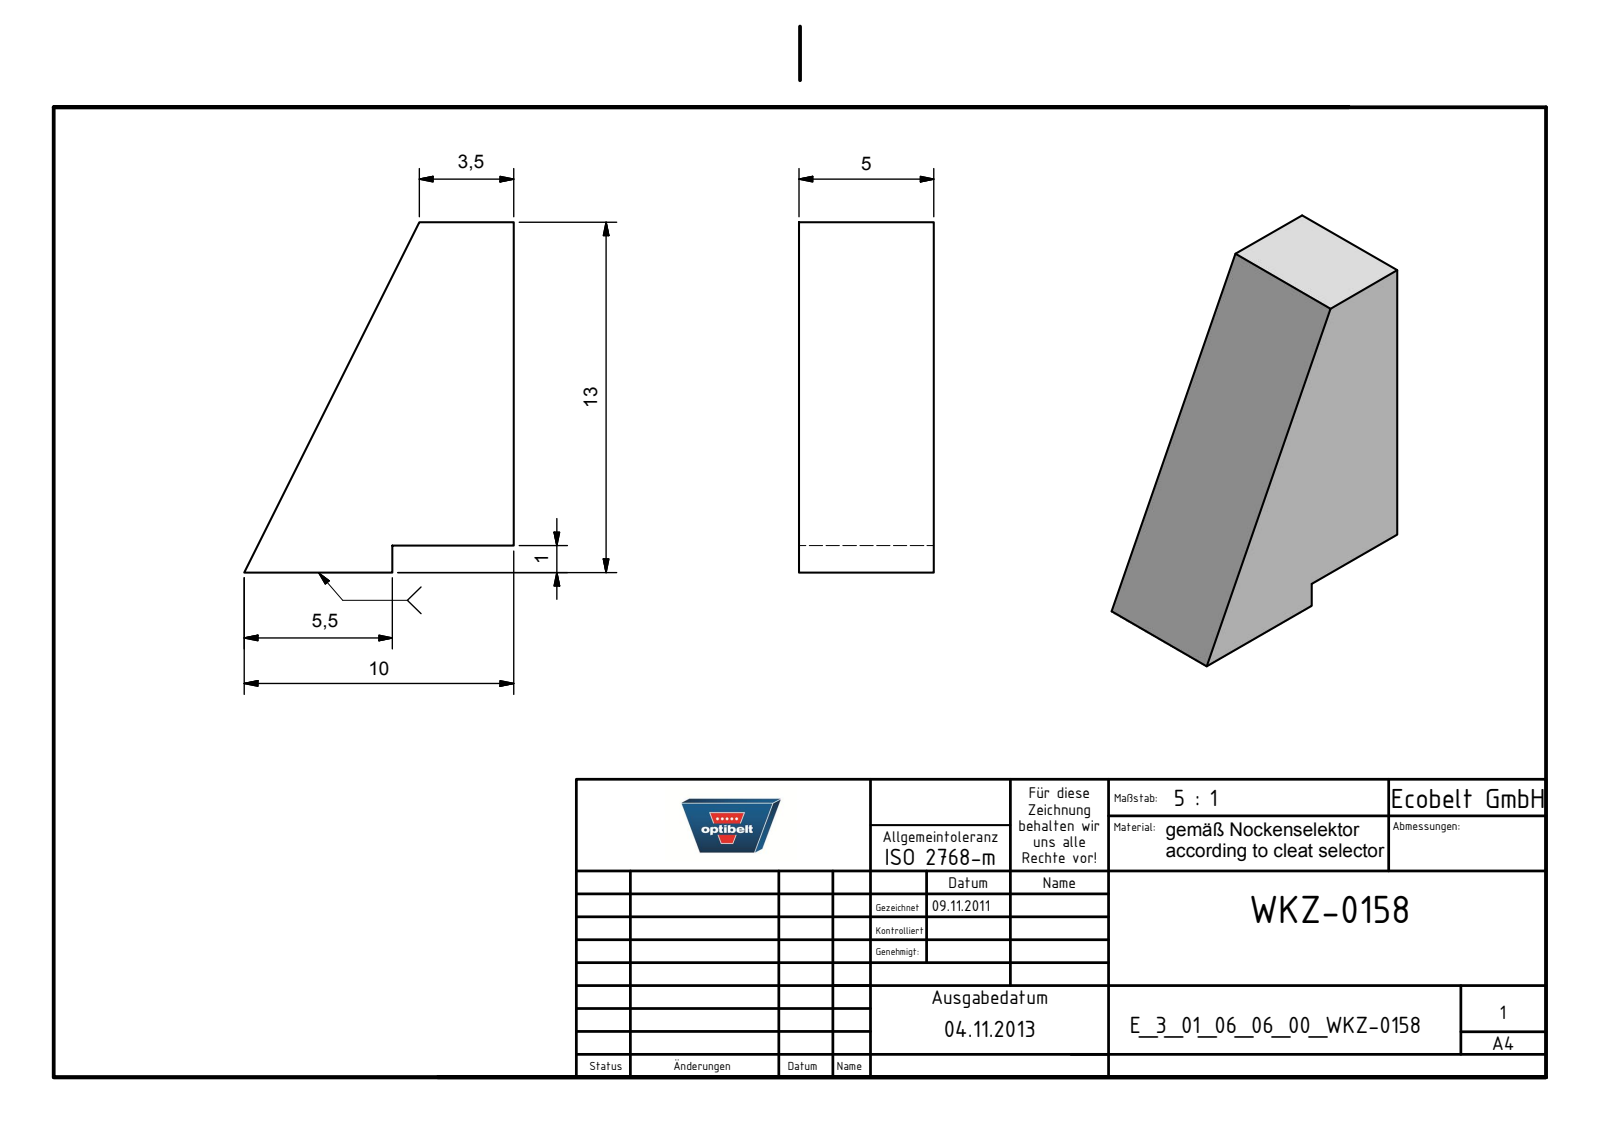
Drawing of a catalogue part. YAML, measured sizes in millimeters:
part_name: "E_3_01_06_06_00_WKZ-0158"
step_written_by: "Autodesk Inventor 2025 (AUTOMOTIVE_DESIGN)"
units: millimeters
bodies: {solids: 1, faces: 8, planar: 8, cylindrical: 0, other: 0}
overall_size: [13, 10, 5]
volume: 416
surface_area: 372
face_to_face_distances: [5, 1, 13, 12, 4.5]
